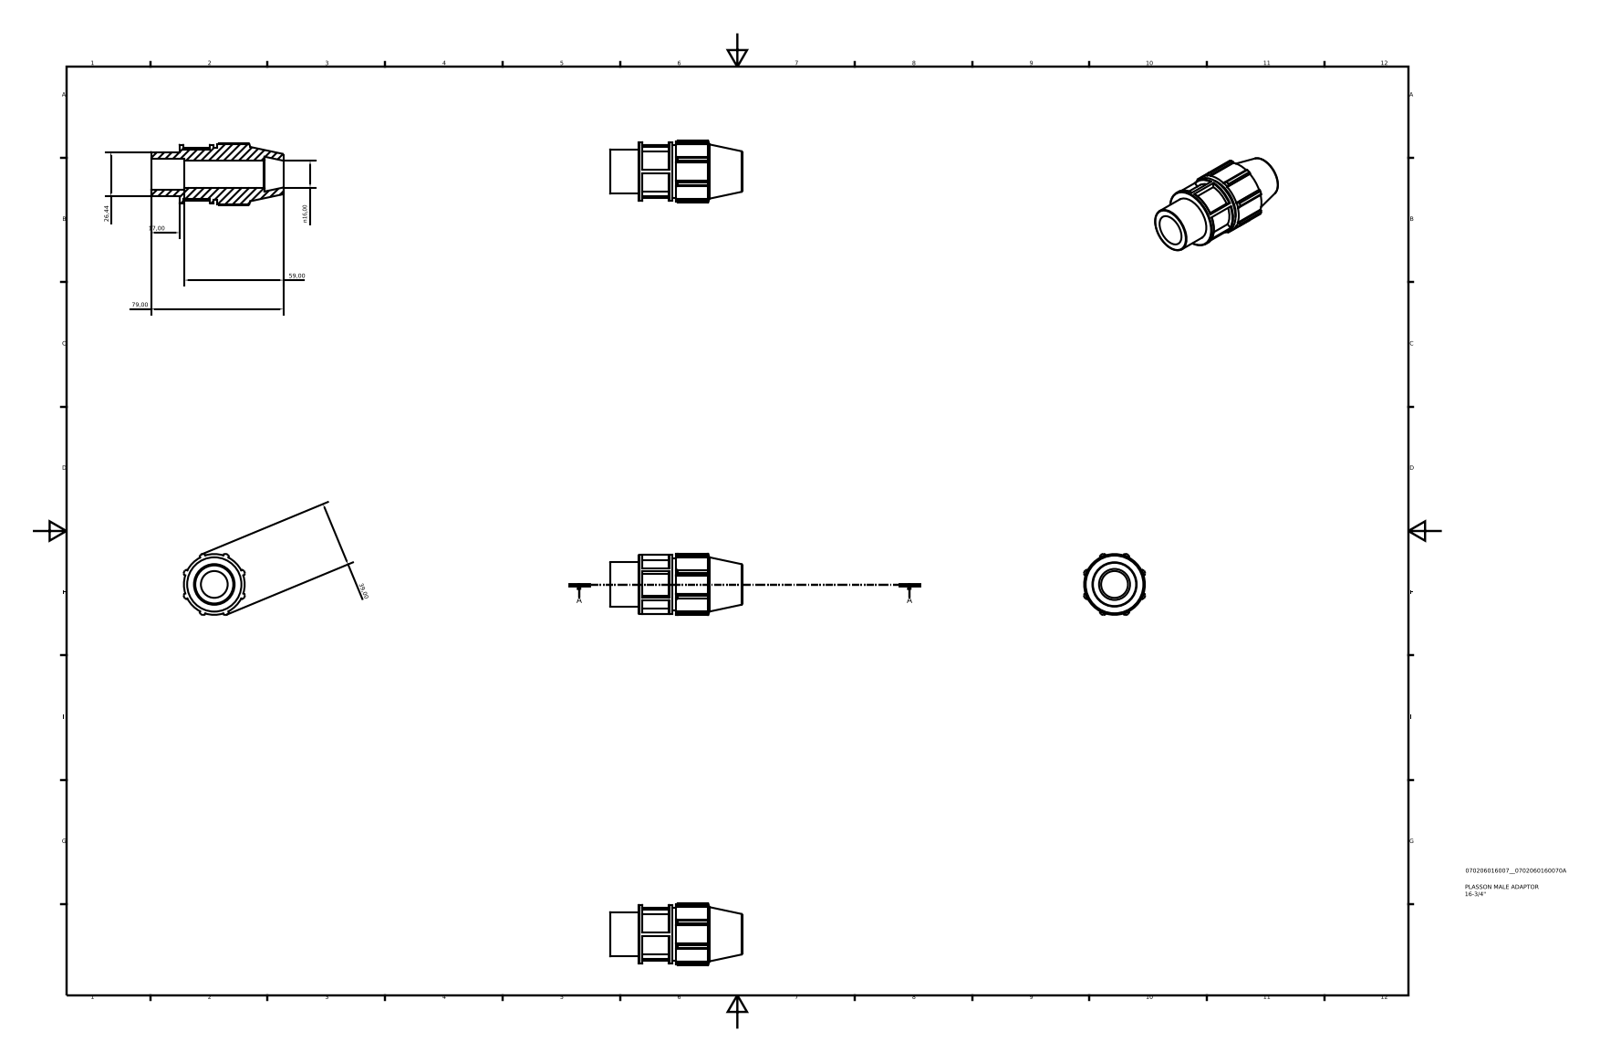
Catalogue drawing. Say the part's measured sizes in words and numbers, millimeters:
The part is named "070206016007". Its 3-D file was written by "Autodesk Inventor 2015 (AUTOMOTIVE_DESIGN)". It is 1 solid with 117 faces: 63 planar, 27 cylindrical and 27 other. Overall it measures 79 by 36.7 by 36.7 millimeters. Its volume is 41 855 cubic millimeters and its surface area 14 955 square millimeters. Round holes: 1 of diameter 16, 1 of diameter 18.51. Round bosses or shafts: 1 of diameter 35.1, 1 of diameter 31.2, 1 of diameter 29.25, 1 of diameter 26.44. Partial cylindrical surfaces (rounded edges, fillets, slot ends): 1 of radius 18.14, 1 of radius 19.5. The main face-to-face distances are 39.5, 1.95, 22.5, 17, 35.06, 18.06, 4.44, 19.26, 2.26, 15.8.
